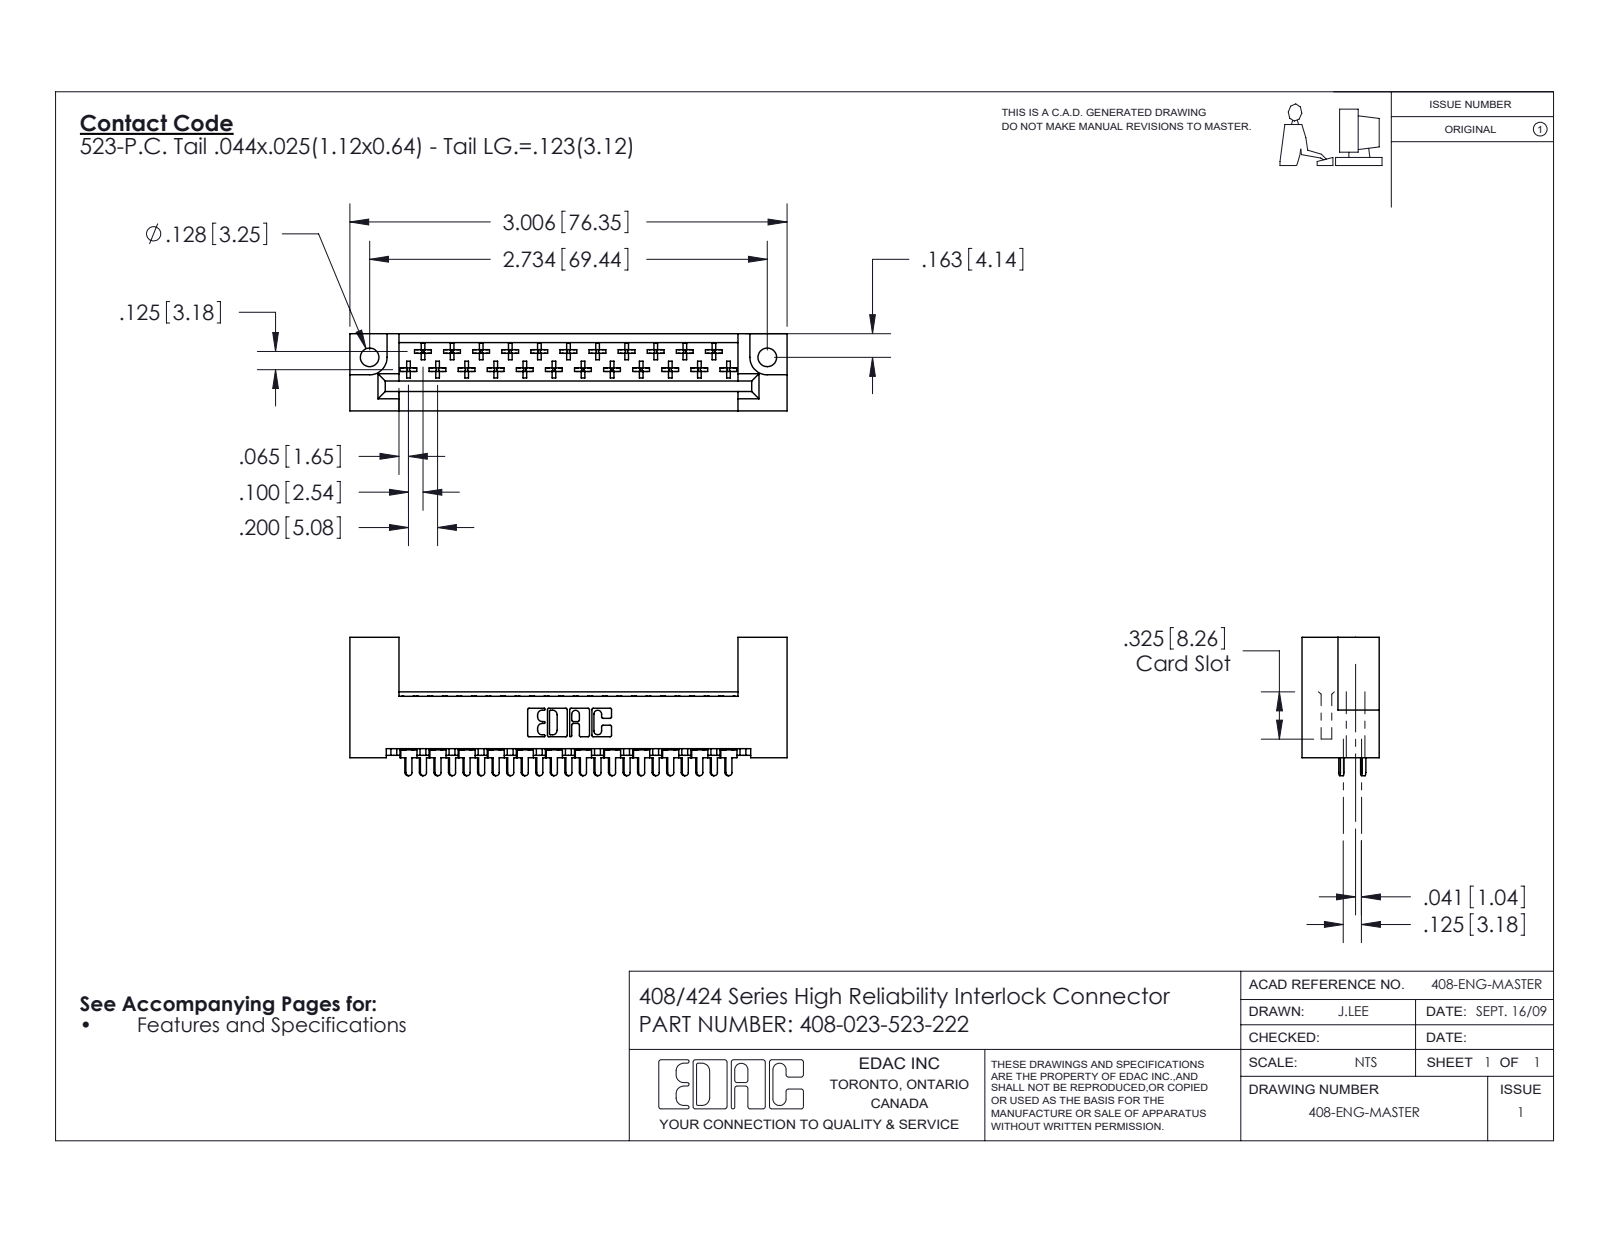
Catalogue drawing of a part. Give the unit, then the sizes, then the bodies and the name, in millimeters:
Units: millimetres
Overall size (bounding box): 76.4 × 24.2 × 13.5
Round holes (diameter × count): ⌀3.3 ×2
Partial cylindrical surfaces — rounded edges, fillets, slot ends (radius × count): R0.3 ×138, R0.5 ×25, R0.6 ×23, R0.3 ×22, R0.2 ×6, R0.8 ×6, R0.7 ×3, R3 ×2
Main face-to-face distances: 13.5, 3.2, 2.5, 0.6, 0.6, 9.2, 10.1, 6, 6.6, 8.3
Hole centre spacings: 69.4
Volume: 9 930 mm³ · Surface area: 10 920 mm²
Bodies: 24 solids, 1404 faces (1055 planar, 257 cylindrical, 92 other)
Part name (STEP PRODUCT): 408-290-001_408-290-123 - Top; 408-290-001_408-290-123 - Bottom; 408 Part_023 - 2; 408-023-523-222
STEP written by: SolidWorks 2016 (CONFIG_CONTROL_DESIGN)
